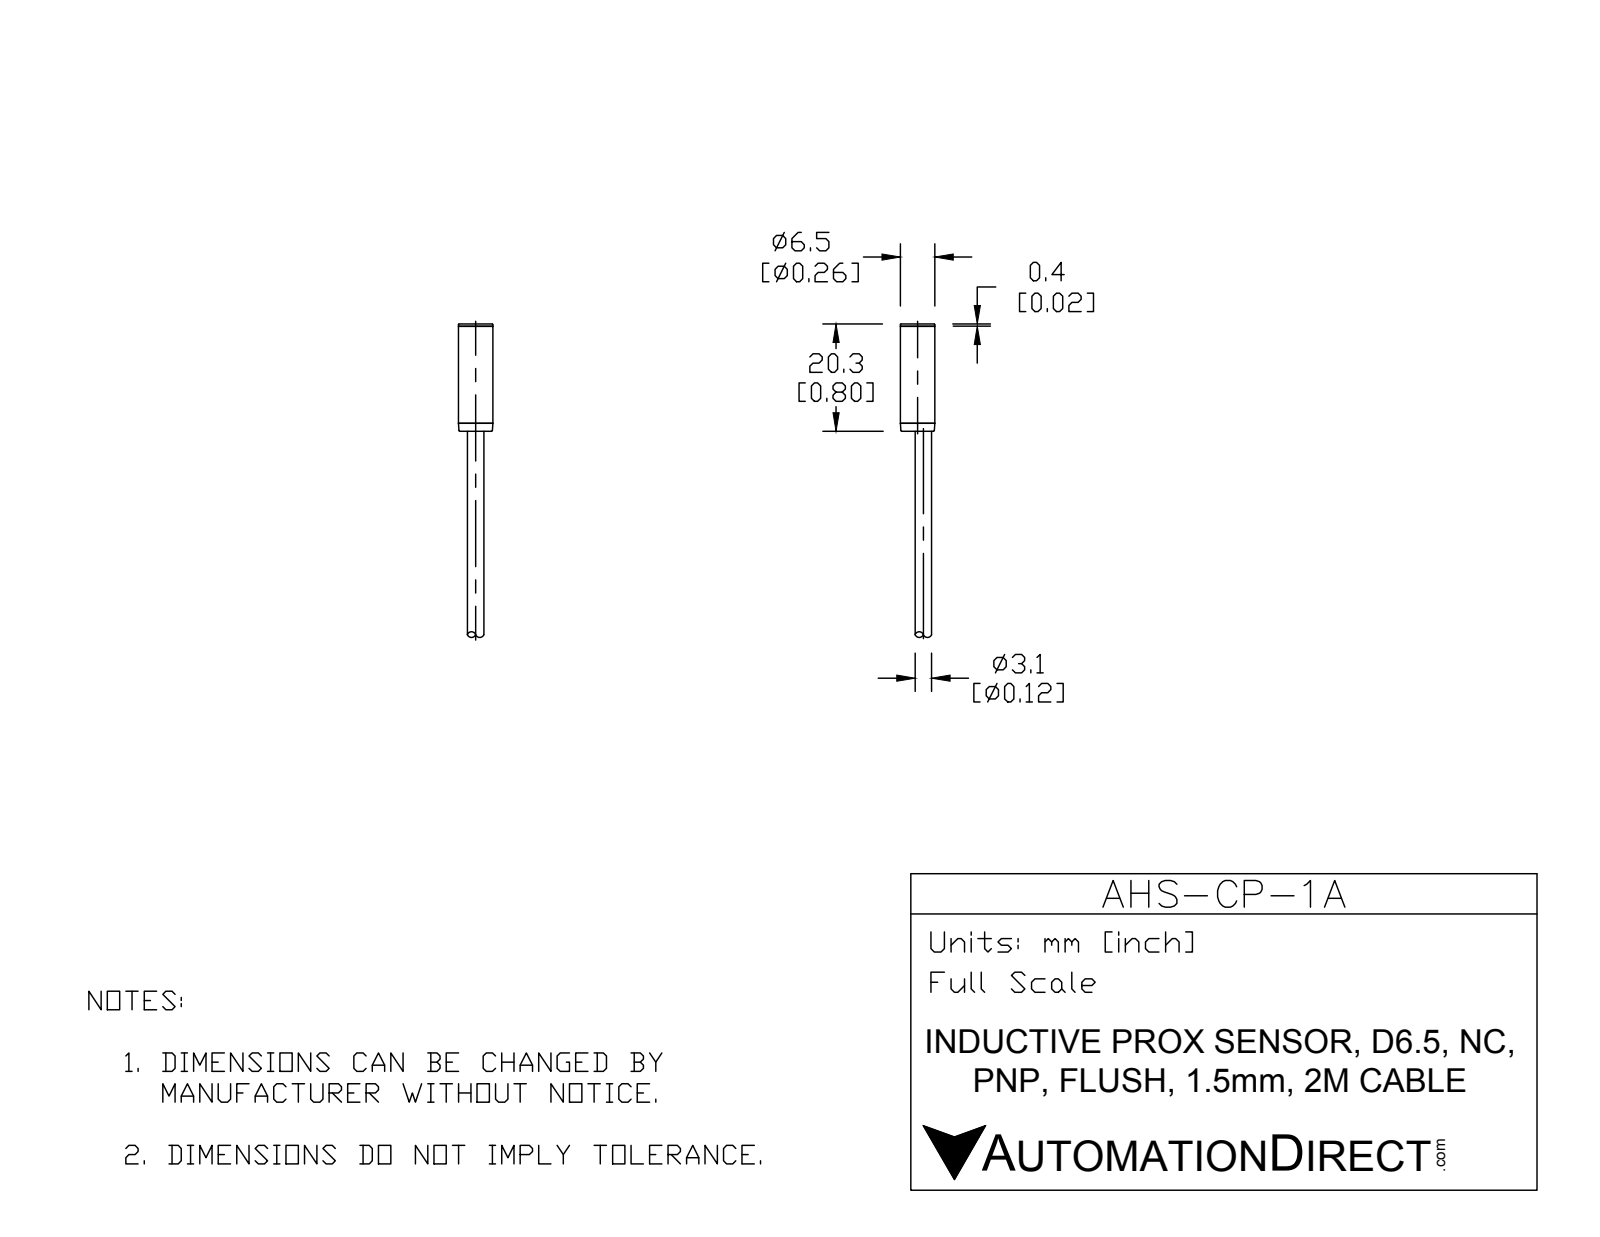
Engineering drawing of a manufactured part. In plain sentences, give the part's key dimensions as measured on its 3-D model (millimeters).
The part is named "AHS-CP-1A". Its 3-D file was written by "SolidWorks 2015 (CONFIG_CONTROL_DESIGN)". It is 2 solids with 17 faces: 5 planar, 6 cylindrical and 6 other. Overall it measures 70.3 by 6.5 by 6.5 millimeters. Its volume is 1 050 cubic millimeters and its surface area 979 square millimeters. Round bosses or shafts: 1 of diameter 6.5, 1 of diameter 3.1. The main face-to-face distances are 20.3, 50, 70.3, 69.9, 19.9, 0.4.
